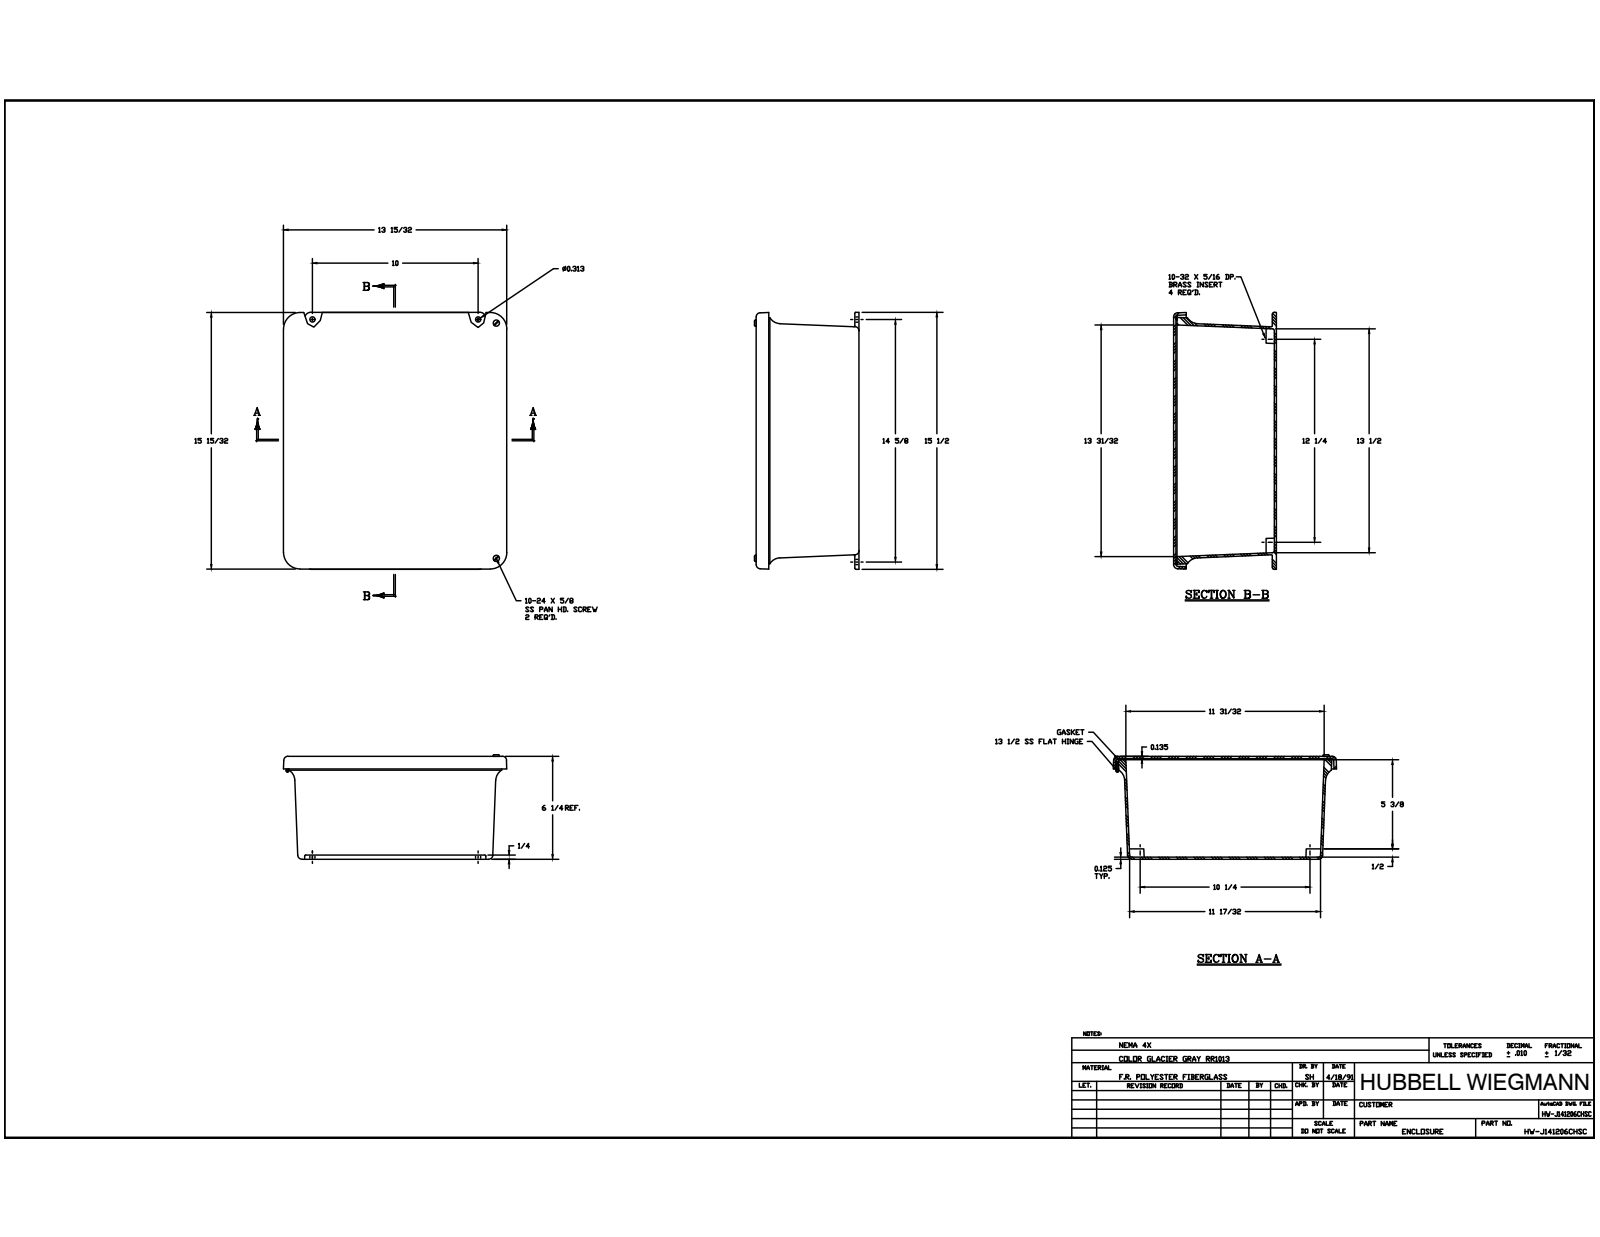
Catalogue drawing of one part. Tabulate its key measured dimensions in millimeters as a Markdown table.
| quantity | value |
| --- | --- |
| part name | J1412HW_1; RMINS45821P_191; RMINS45821P_192; RMINS45821P_193 (+8 more) |
| STEP written by | Autodesk Inventor 2014 (AUTOMOTIVE_DESIGN) |
| units | millimeters |
| bodies | 24 solids, 866 faces (317 planar, 338 cylindrical, 211 other) |
| overall size | 393.7 × 342.99 × 161.13 |
| volume | 1 851 000 mm³ |
| surface area | 1 013 000 mm² |
| round holes (diameter × count) | 3.33 × 10, 3.56 × 10, 3.86 × 8, 3.96 × 4, 5.54 × 4, 3.68 × 2, 2.16 × 1 |
| round bosses / shafts (diameter × count) | 6.35 × 10, 3.17 × 10, 6.86 × 6, 4.83 × 2, 3.97 × 2, 3.94 × 1 |
| partial cylindrical surfaces (radius × count) | 0.79 × 20, 3.17 × 12, 6.35 × 12, 5.08 × 6, 9.53 × 4, 19.05 × 4, 1.6 × 2 |
| main face-to-face distances | 3.18, 3.42, 154.38, 157.8, 151.2, 154.62, 3.17, 8.38, 3.86, 152.4 |
| hole center spacings | 82.55, 165.1, 247.65, 6.35, 76.2, 34.8, 158.75, 286.01 |
